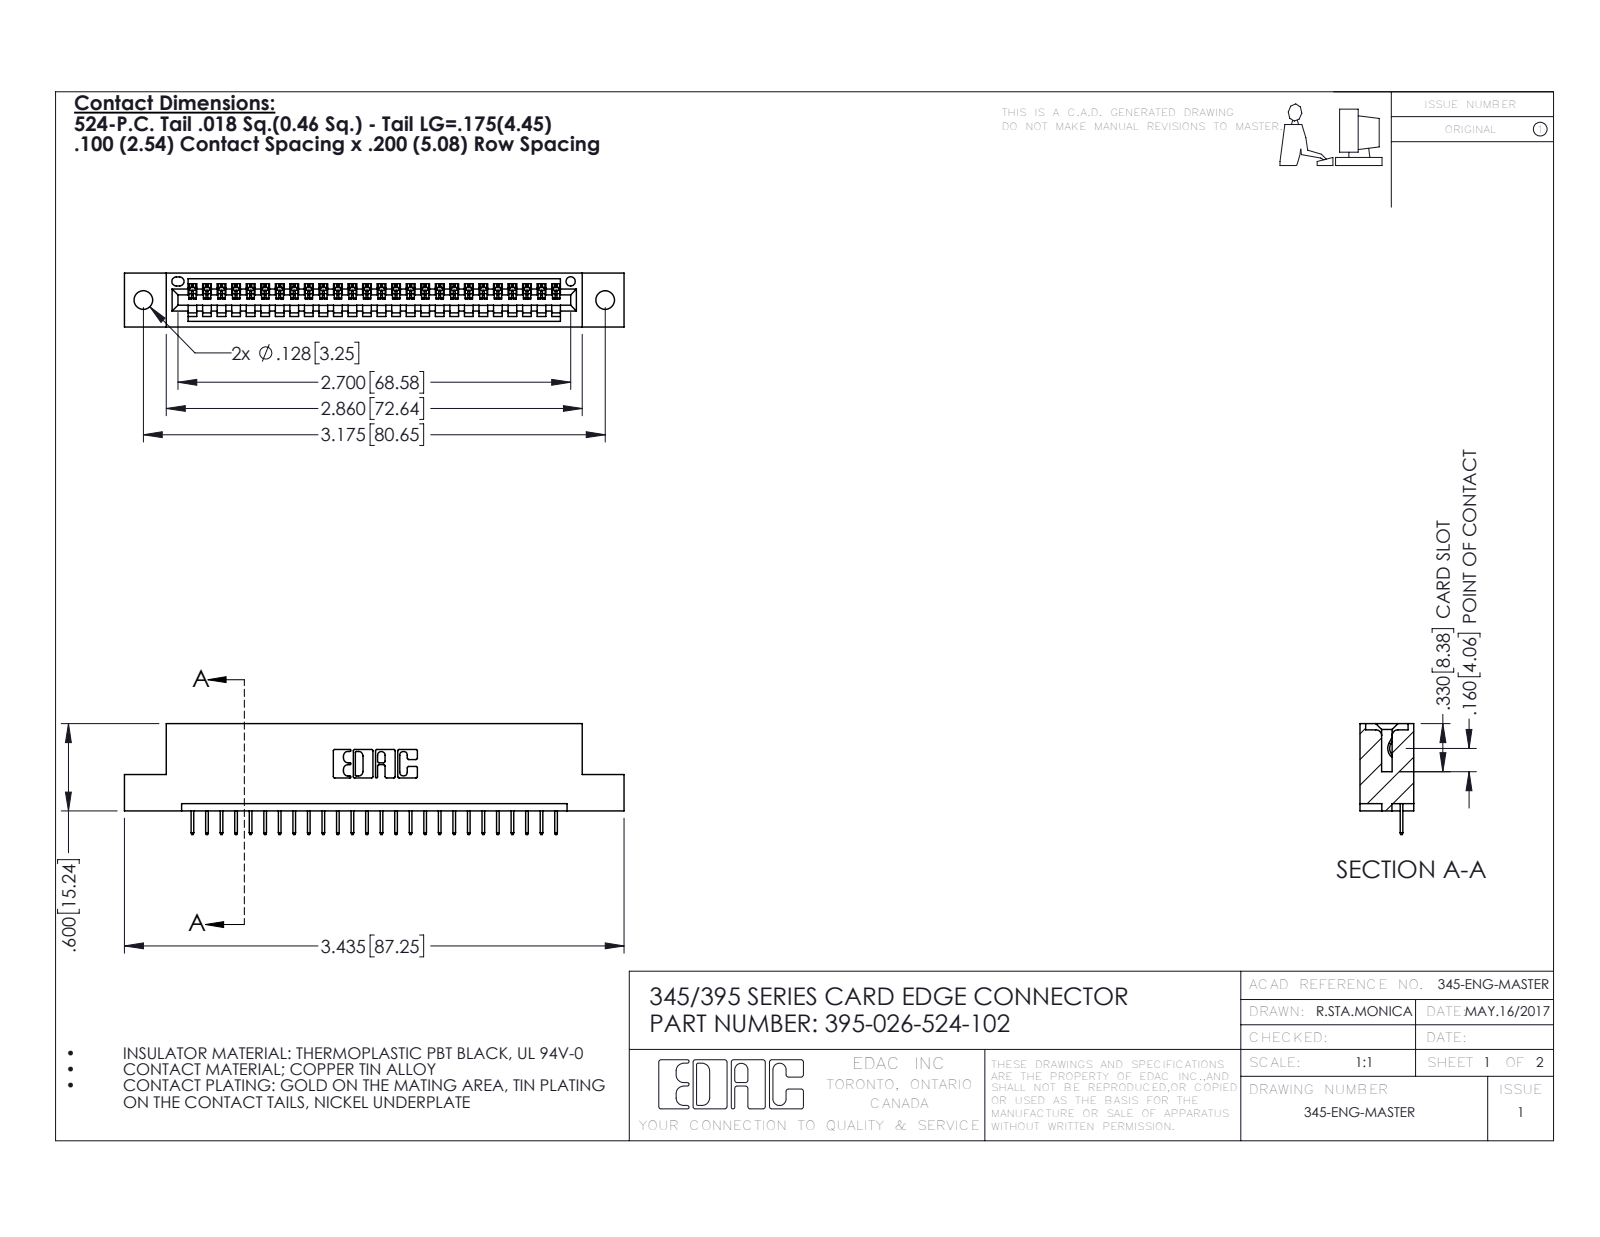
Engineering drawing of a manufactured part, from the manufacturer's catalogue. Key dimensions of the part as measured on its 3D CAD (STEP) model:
Part name (STEP PRODUCT): 345 Part_Flush Mounting Lugs - 0.128 Dia; 395-026-524-102; 345-292-001_345-293-124
STEP written by: SolidWorks 2016 (CONFIG_CONTROL_DESIGN)
Units: inches
Bodies: 27 solids, 1738 faces (1276 planar, 462 cylindrical, 0 other)
Overall size (bounding box): 3.435 × 0.762 × 0.37
Volume: 0.489 in³ · Surface area: 15.25 in²
Round holes (diameter × count): ⌀0.128 ×2, ⌀0.064 ×1
Partial cylindrical surfaces — rounded edges, fillets, slot ends (radius × count): R0.006 ×52, R0.01 ×22, R0.007 ×6, R0.031 ×6, R0.026 ×3, R0.031 ×2, R0.04 ×2, R0.014 ×1
Main face-to-face distances: 0.298, 0.072, 0.37, 0.2, 0.098, 0.272, 0.025, 0.225, 0.072, 0.149
Hole centre spacings: 0.27, 2.94, 3.175
